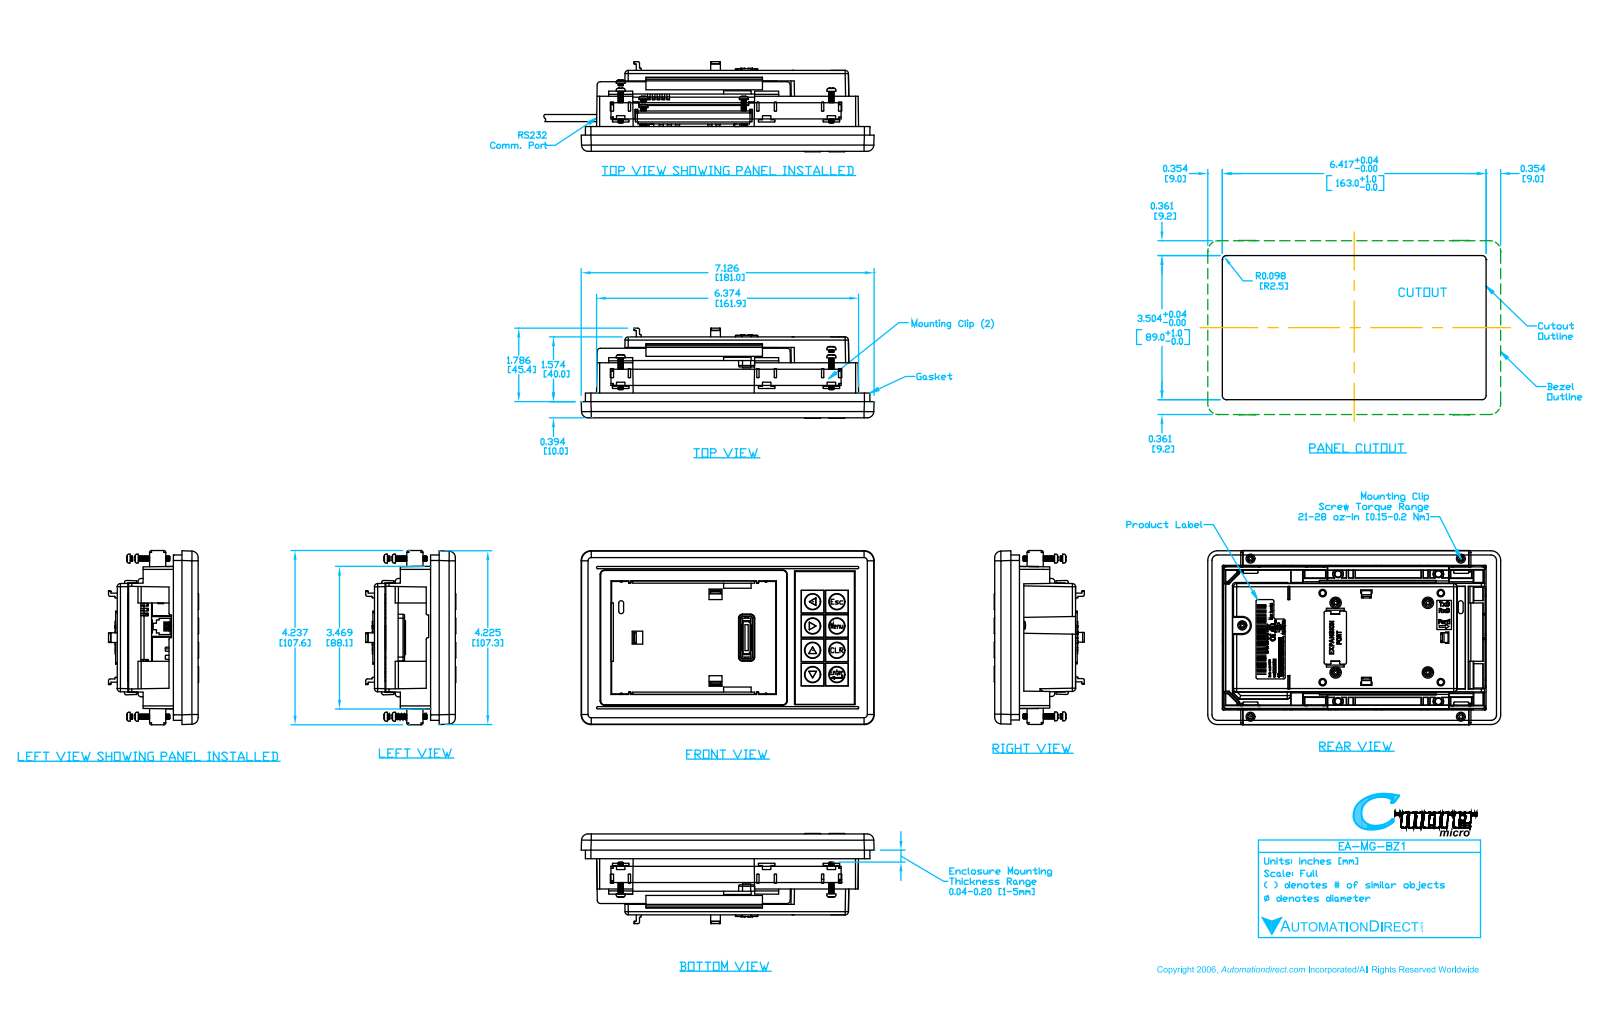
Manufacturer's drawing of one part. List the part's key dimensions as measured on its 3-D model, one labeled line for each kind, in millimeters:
Part name (STEP PRODUCT): EA-MG-BZ2
STEP written by: SolidWorks 2009 (CONFIG_CONTROL_DESIGN)
Units: millimetres
Bodies: 26 solids, 718 faces (546 planar, 80 cylindrical, 92 other)
Overall size (bounding box): 207 × 107.6 × 55.65
Volume: 325 124 mm³ · Surface area: 127 430 mm²
Partial cylindrical surfaces — rounded edges, fillets, slot ends (radius × count): R2 ×32, R1 ×14, R0.5 ×8, R2.25 ×4, R3 ×4, R5 ×4, R1.8 ×2, R5.25 ×1
Main face-to-face distances: 0.5, 8, 50, 49.5, 7.85, 6.7, 42.8, 43.3, 14.7, 34.8
